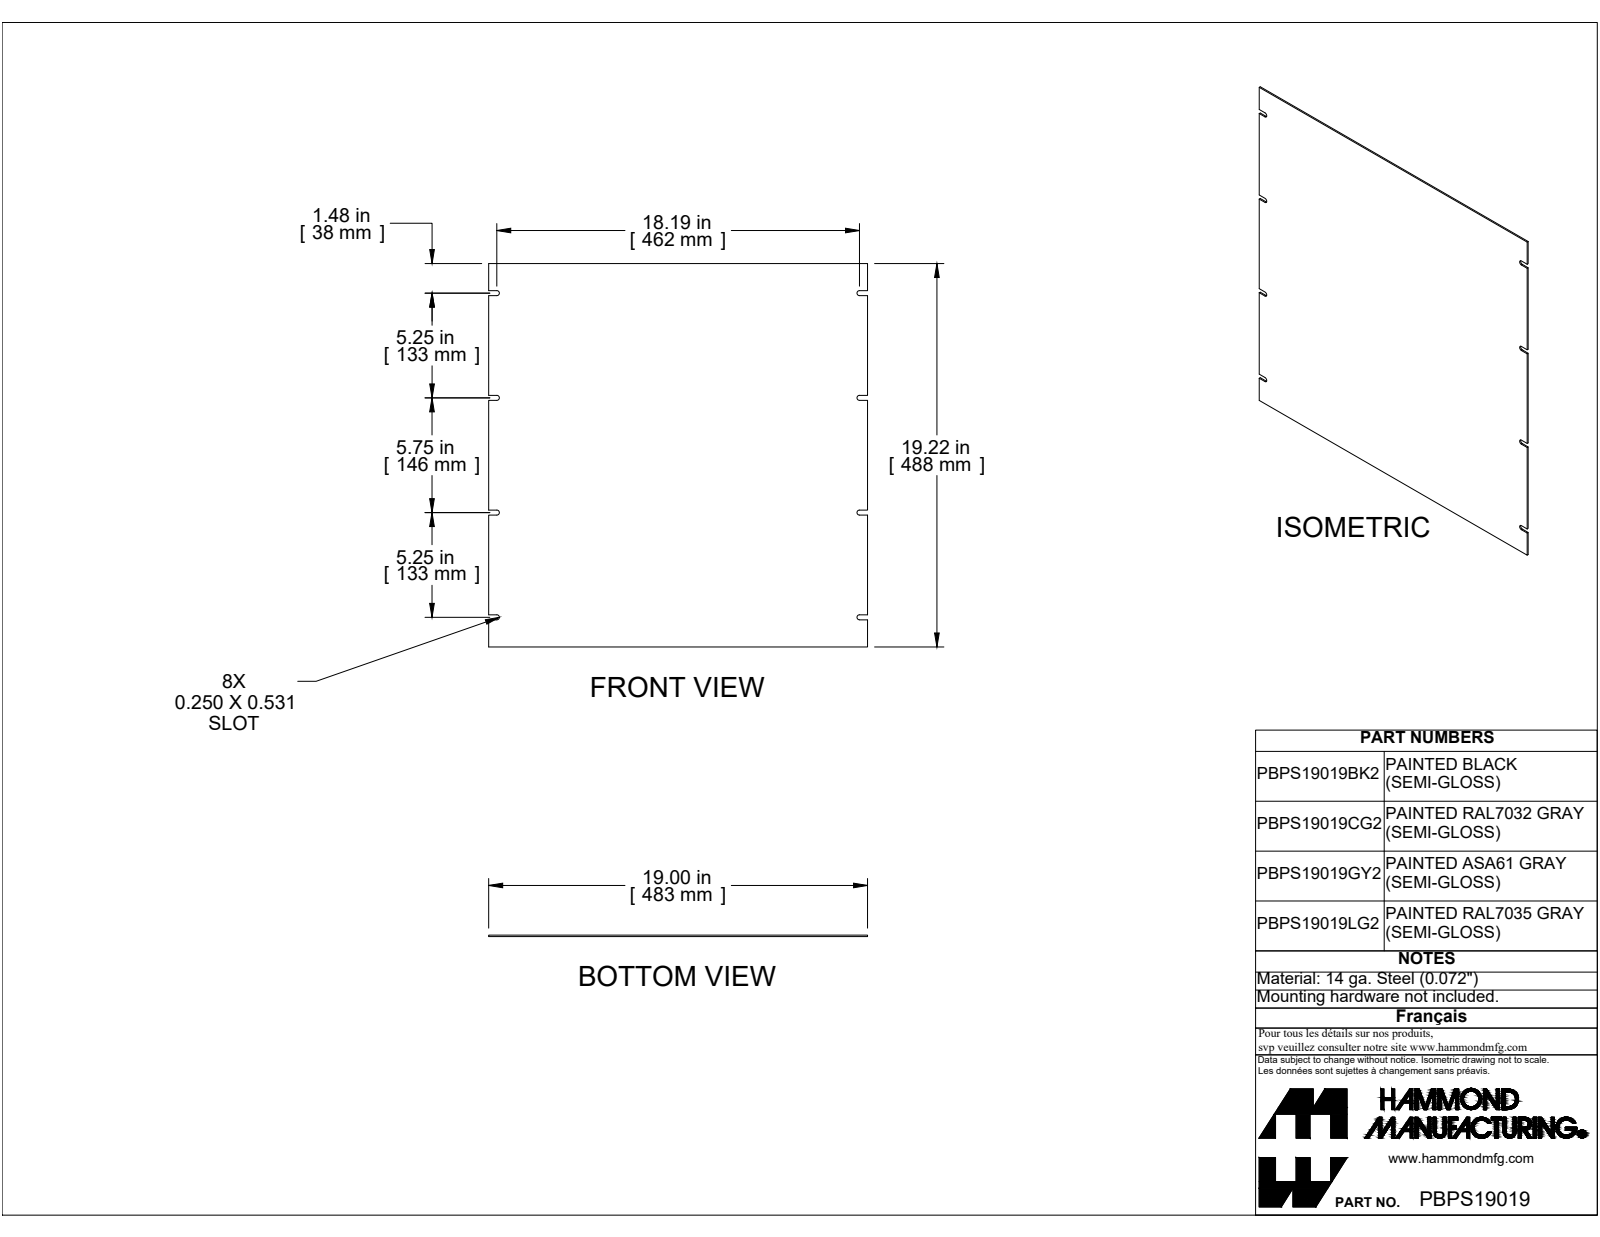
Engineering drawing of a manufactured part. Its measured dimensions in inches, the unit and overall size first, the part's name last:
Units: inches
Overall size (bounding box): 19.218 × 19 × 0.072
Partial cylindrical surfaces — rounded edges, fillets, slot ends (radius × count): R0.125 ×8
Main face-to-face distances: 0.072, 19.218, 19, 0.25, 5.25, 11, 5.5, 6.609, 12.609, 6.859
Volume: 26.22 in³ · Surface area: 734.3 in²
Bodies: 1 solid, 38 faces (30 planar, 8 cylindrical, 0 other)
Part name (STEP PRODUCT): PBPS19019BK2
STEP written by: SolidWorks 2019 (CONFIG_CONTROL_DESIGN)
